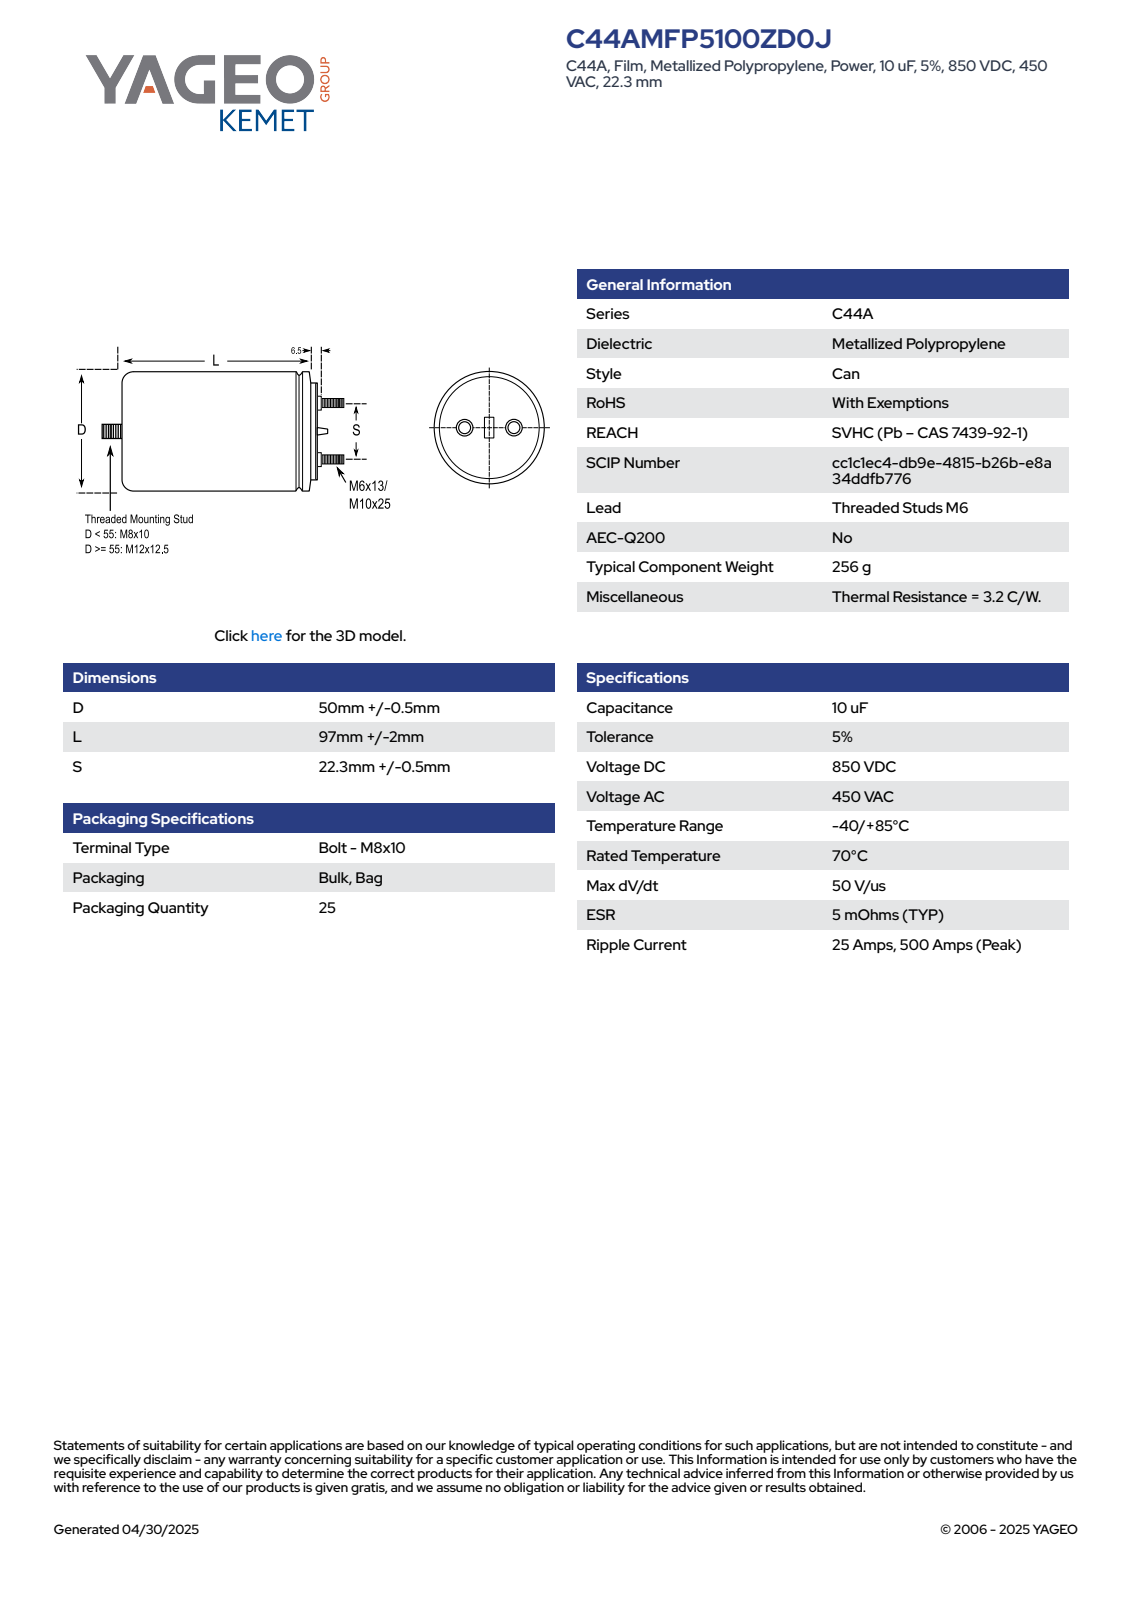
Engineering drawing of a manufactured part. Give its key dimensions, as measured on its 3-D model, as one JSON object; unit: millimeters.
{"part_name": "CFP_C44A_50X97_D50.5L99S22.3", "step_written_by": "SolidWorks 2014 (AUTOMOTIVE_DESIGN)", "units": "millimeters", "bodies": {"solids": 1, "faces": 102, "planar": 29, "cylindrical": 34, "other": 39}, "overall_size": [128.5, 50.5, 50.5], "volume_mm3": 204296, "surface_area_mm2": 20951, "round_bosses_or_shafts": [[9, 2], [6, 2], [50.5, 1], [39.61, 1], [8, 1]], "partial_cylinders_radius": [[25.24, 1]], "face_to_face_distances": [104, 105.5, 1.5, 118.5, 14.5, 13, 10, 114, 115.5, 128.5]}
